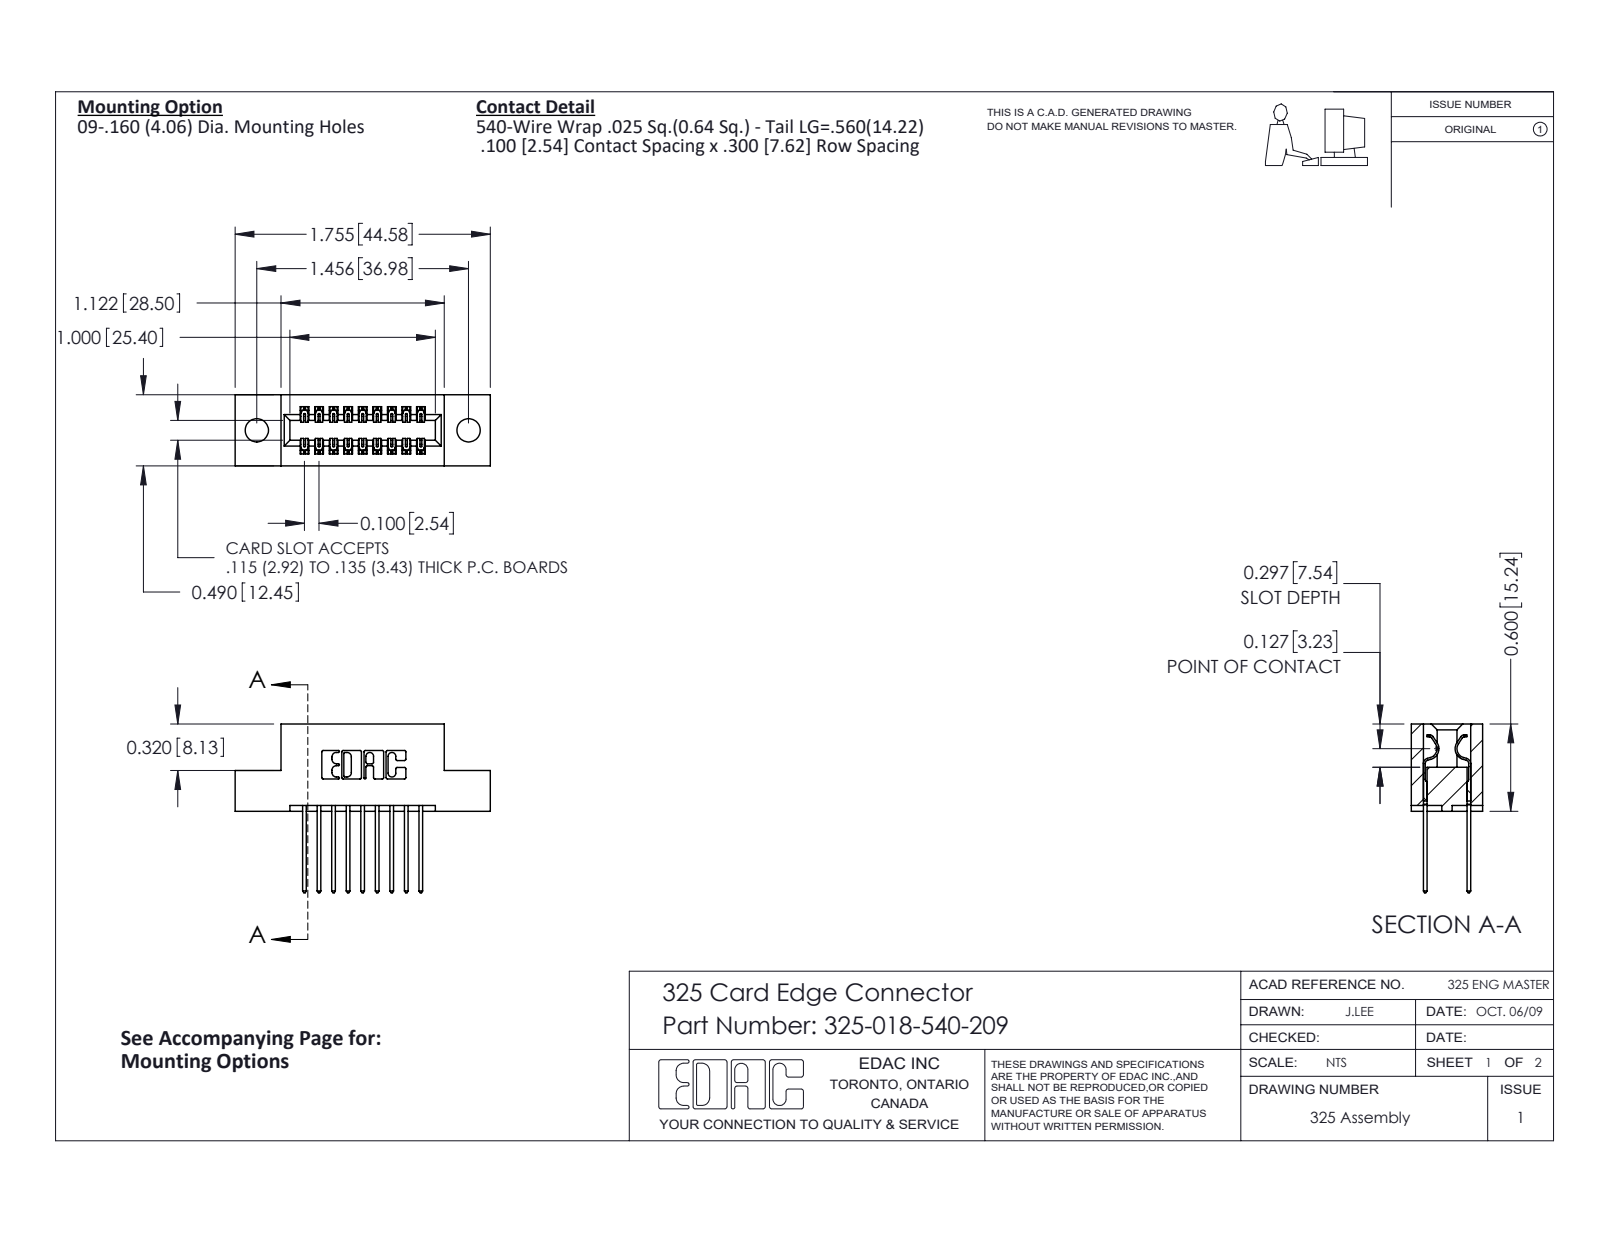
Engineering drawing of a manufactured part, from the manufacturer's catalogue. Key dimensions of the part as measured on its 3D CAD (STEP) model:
Part name (STEP PRODUCT): 325 Part_.160 TH; 325-018-540-209; 325-292-001_325-293-140
STEP written by: SolidWorks 2016 (CONFIG_CONTROL_DESIGN)
Units: inches
Bodies: 19 solids, 1050 faces (718 planar, 332 cylindrical, 0 other)
Overall size (bounding box): 1.755 × 1.16 × 0.49
Volume: 0.323 in³ · Surface area: 9.103 in²
Round holes (diameter × count): ⌀0.16 ×2
Partial cylindrical surfaces — rounded edges, fillets, slot ends (radius × count): R0.006 ×27, R0.01 ×22, R0.01 ×18, R0.007 ×6, R0.031 ×6, R0.026 ×3, R0.014 ×2, R0.022 ×2
Main face-to-face distances: 0.3, 0.083, 0.407, 0.04, 0.1, 0.49, 0.2, 0.107, 0.383, 0.025
Hole centre spacings: 1.456
